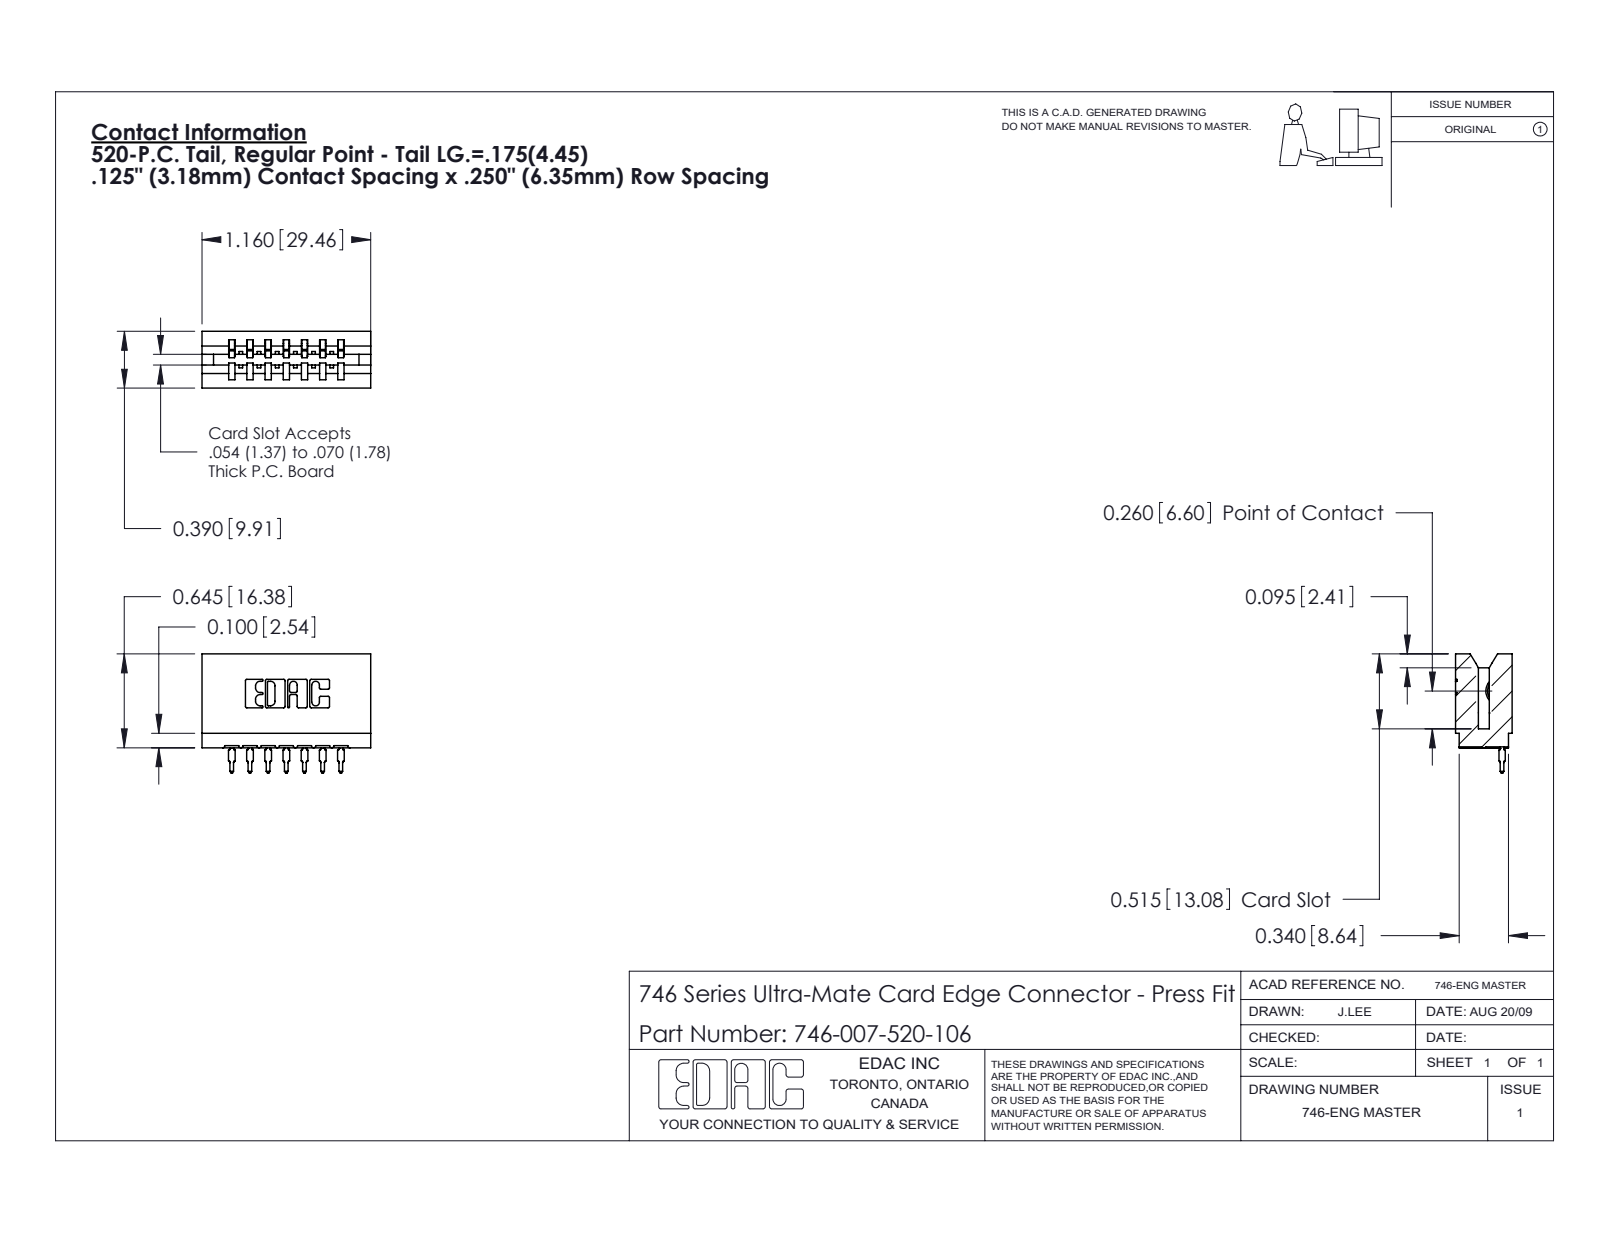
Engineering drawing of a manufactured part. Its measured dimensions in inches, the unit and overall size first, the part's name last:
Units: inches
Overall size (bounding box): 1.16 × 0.819 × 0.39
Partial cylindrical surfaces — rounded edges, fillets, slot ends (radius × count): R0.01 ×22, R0.021 ×14, R0.015 ×8, R0.007 ×6, R0.031 ×6, R0.005 ×4, R0.011 ×4, R0.026 ×3
Main face-to-face distances: 0.25, 0.042, 0.333, 0.5, 0.125, 0.125, 0.057, 0.208, 0.292, 0.39
Volume: 0.2 in³ · Surface area: 6.579 in²
Bodies: 8 solids, 854 faces (497 planar, 175 cylindrical, 182 other)
Part name (STEP PRODUCT): 746-007-520-106; 746 Part_.515 Slot Depth - 06; 746-292-001_520
STEP written by: SolidWorks 2020 (CONFIG_CONTROL_DESIGN)
